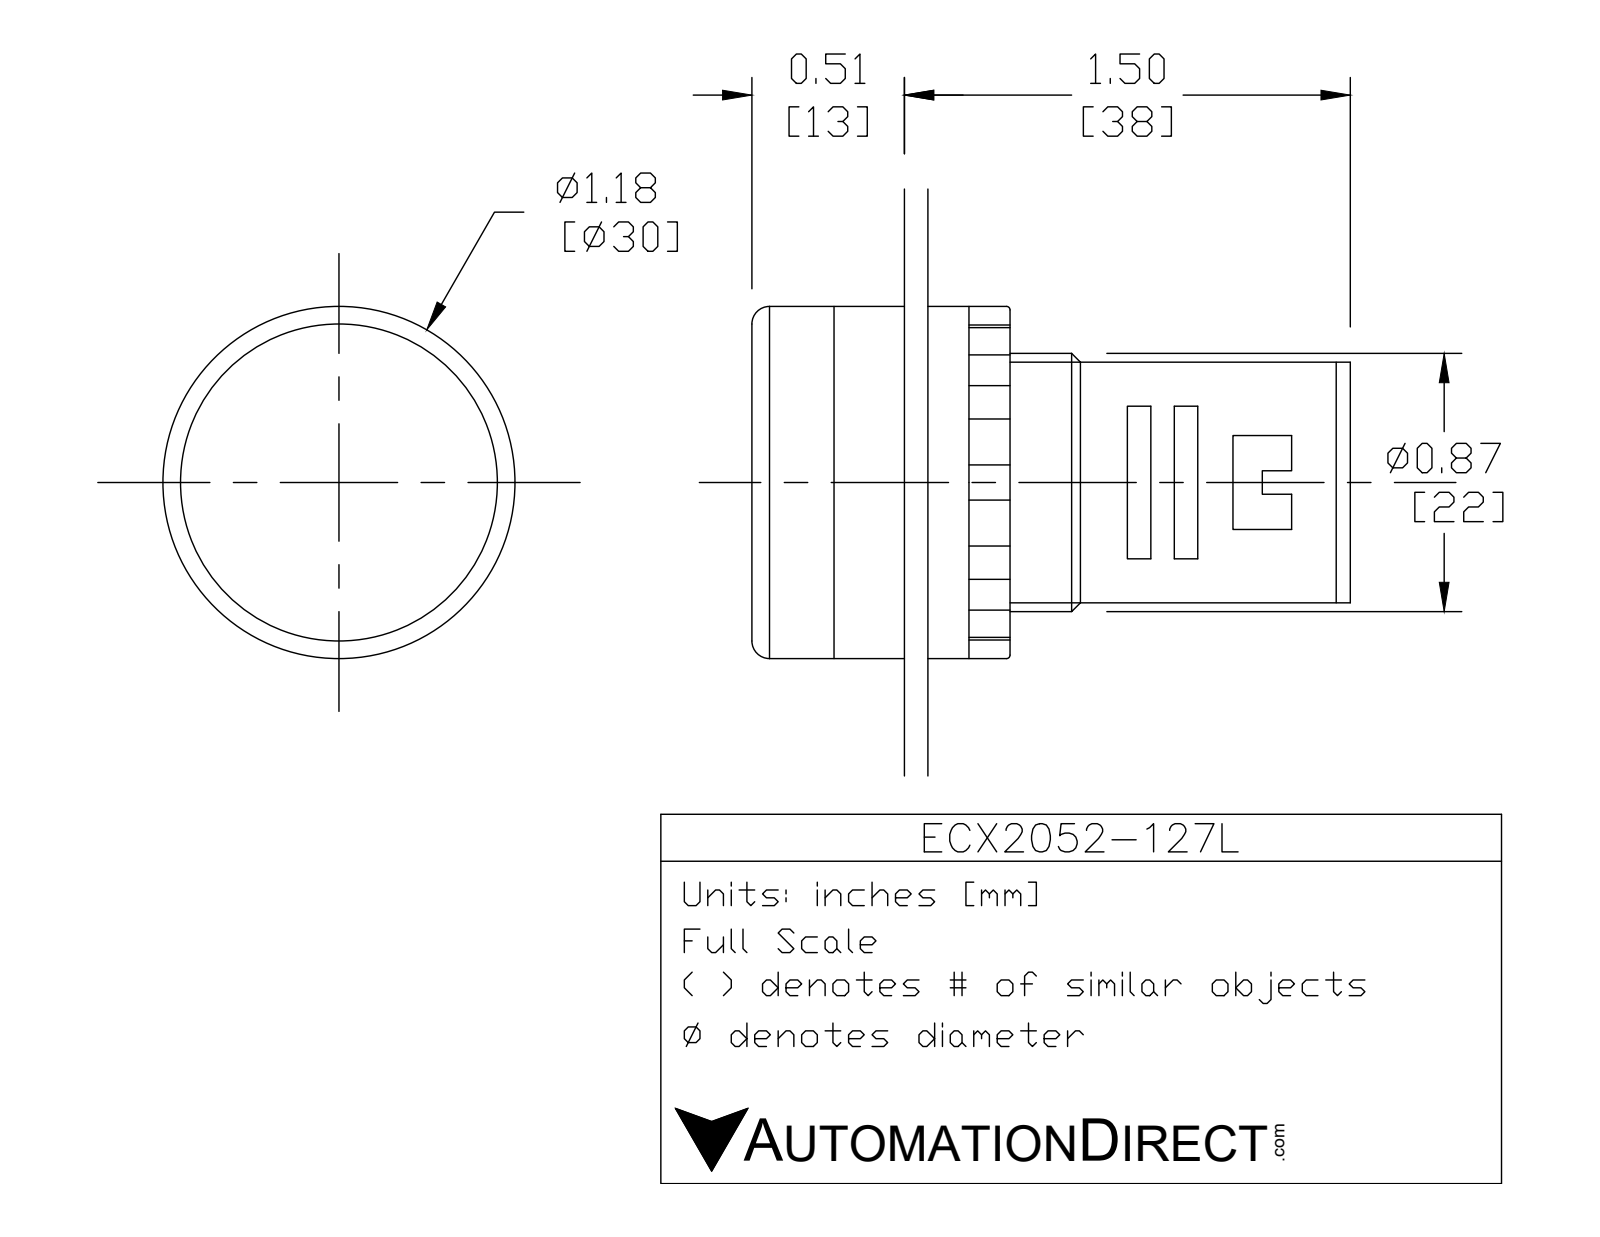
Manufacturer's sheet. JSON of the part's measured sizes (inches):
{"part_name": "ECX2052-127L", "step_written_by": "SolidWorks 2017 (AUTOMOTIVE_DESIGN)", "units": "inches", "bodies": {"solids": 6, "faces": 123, "planar": 63, "cylindrical": 39, "other": 21}, "overall_size": [2.008, 1.181, 1.181], "volume_in3": 1.372, "surface_area_in2": 15.24, "round_holes": [[0.217, 2], [0.886, 1]], "round_bosses_or_shafts": [[0.157, 2], [1.181, 1], [1.142, 1], [1.043, 1], [0.866, 1], [0.787, 1]], "partial_cylinders_radius": [[0.039, 12]], "face_to_face_distances": [0.236, 0.748, 0.512, 0.276, 0.079, 0.984, 0.157, 0.472, 0.669, 0.591], "hole_center_spacings": [0.182, 0.364]}
